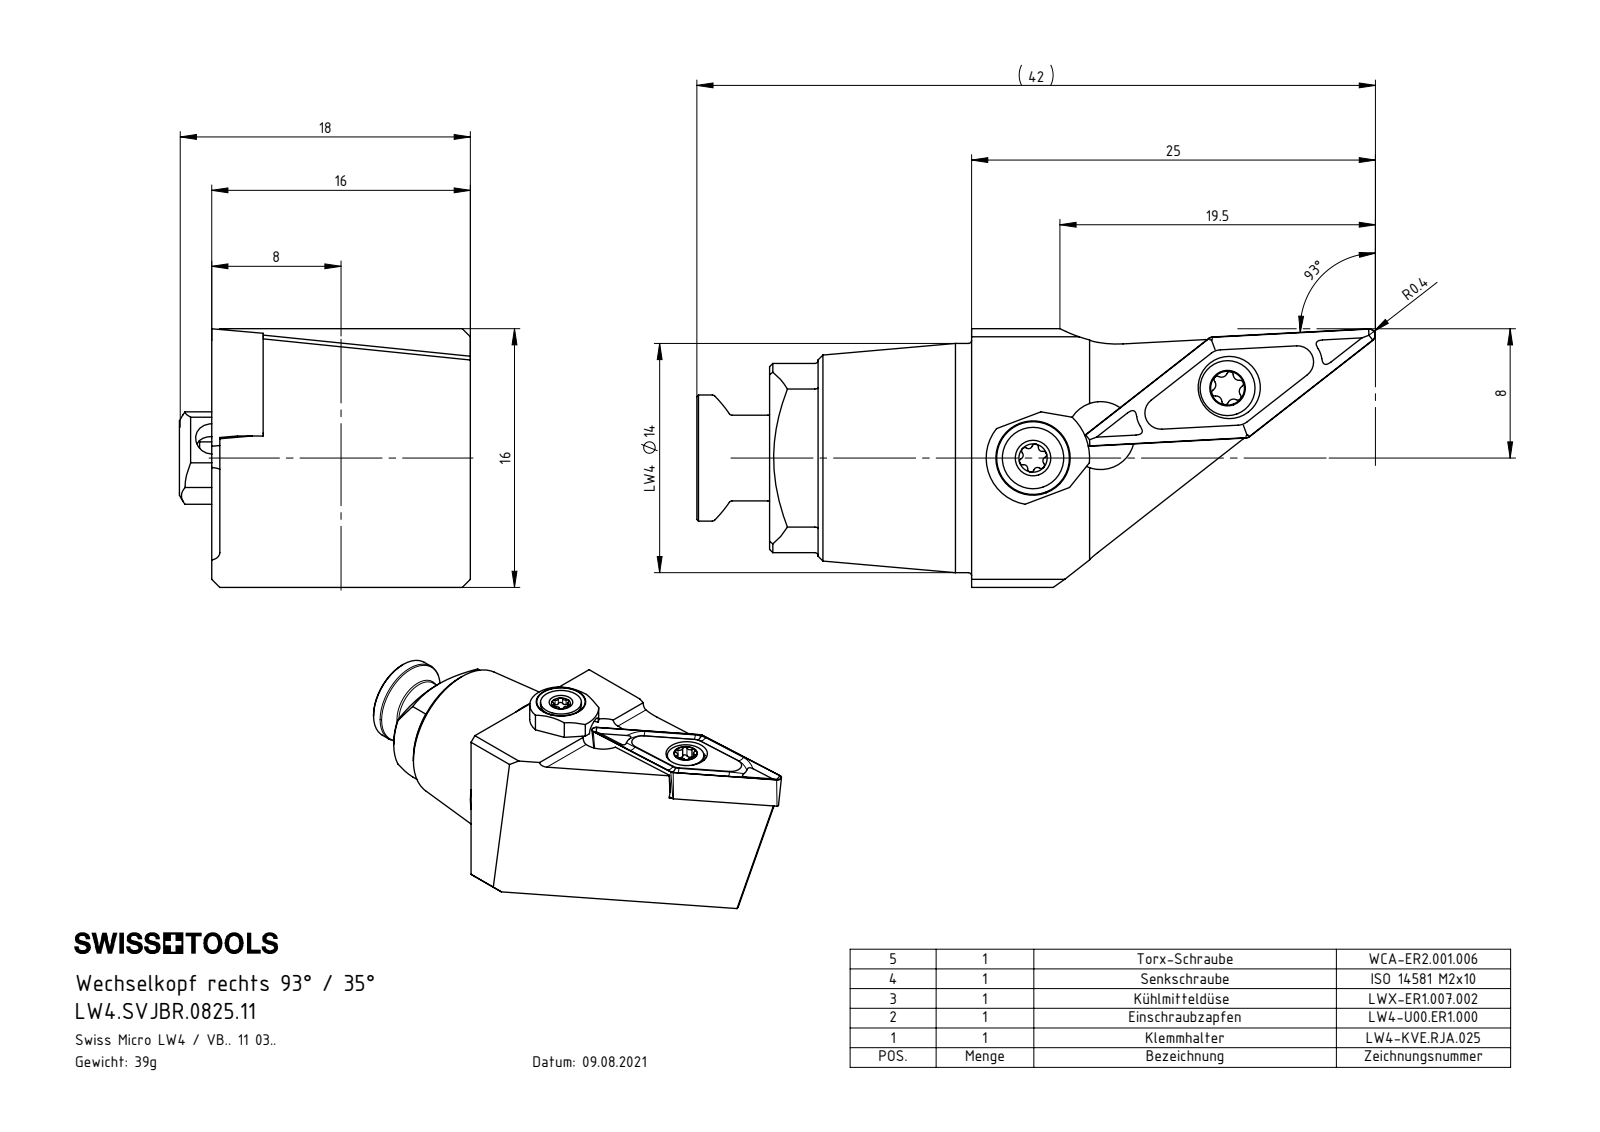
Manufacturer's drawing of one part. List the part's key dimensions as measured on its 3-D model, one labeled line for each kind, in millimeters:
Part name (STEP PRODUCT): LW4.SVJBR.0825.11; LW4-KVE.RJA.025_A; WCA-ER2.001.006_A; ISO 14581 - M2x10 (+1 more)
STEP written by: SolidWorks 2022 (CONFIG_CONTROL_DESIGN)
Units: millimetres
Bodies: 4 solids, 205 faces (56 planar, 68 cylindrical, 81 other)
Overall size (bounding box): 37.48 × 17.95 × 16
Volume: 4 502 mm³ · Surface area: 2 722 mm²
Round holes (diameter × count): ⌀2 ×2, ⌀1.6 ×1, ⌀2.05 ×1, ⌀2.8 ×1, ⌀3 ×1, ⌀3.85 ×1, ⌀4.2 ×1, ⌀5.5 ×1
Round bosses / shafts (diameter × count): ⌀14.17 ×1, ⌀3.8 ×1, ⌀3.4 ×1, ⌀2.5 ×1, ⌀2 ×1
Partial cylindrical surfaces — rounded edges, fillets, slot ends (radius × count): R0.2 ×8, R0.21 ×6, R0.24 ×6, R0.36 ×4, R0.36 ×2, R0.5 ×1, R5.85 ×1, R7 ×1
Main face-to-face distances: 16, 12.82, 3.18, 15.5, 2.68, 0.5, 12.5, 4, 12, 3
Hole centre spacings: 4.41, 8.38, 8.49, 12.79, 12.9
